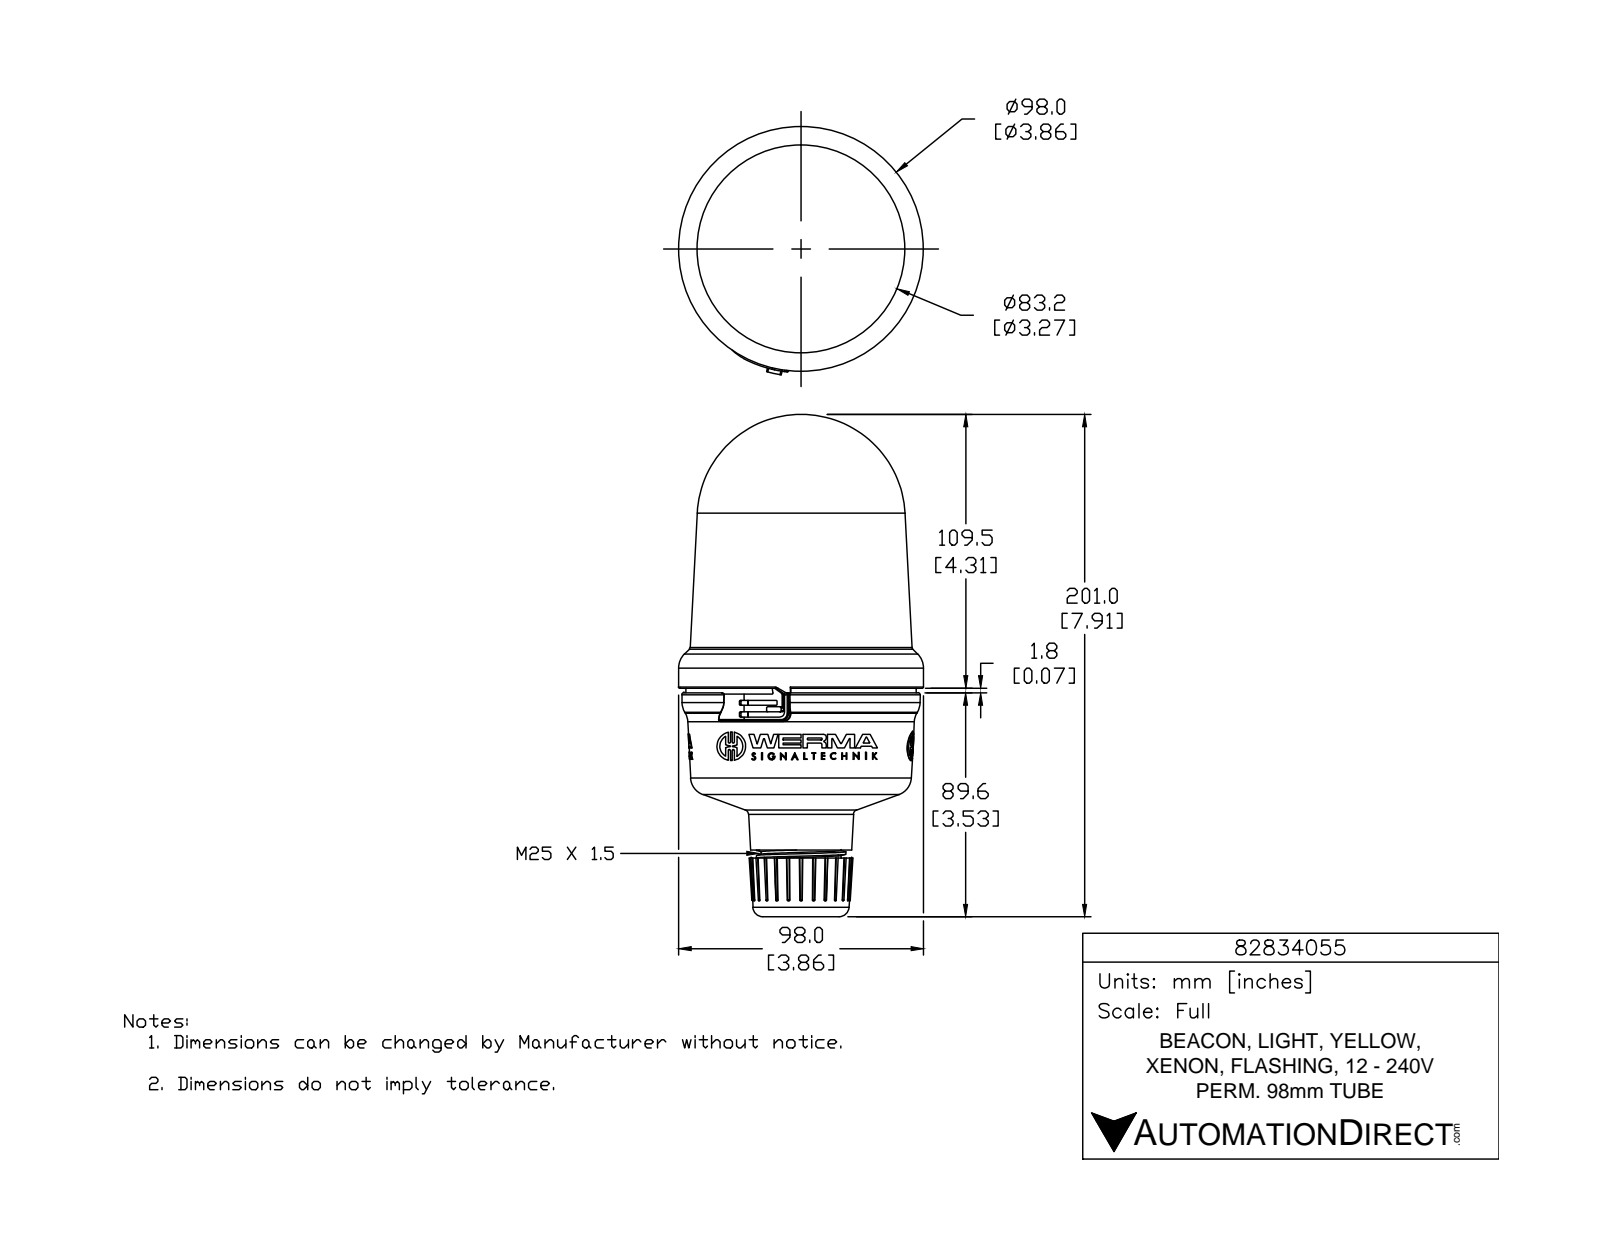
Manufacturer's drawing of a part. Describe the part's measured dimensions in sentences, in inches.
The part is named "82834055". Its 3-D file was written by "SolidWorks 2015 (AUTOMOTIVE_DESIGN)". It is 1 solid with 1006 faces: 554 planar, 189 cylindrical and 263 other. Overall it measures 7.914 by 3.912 by 3.858 inches. Its volume is 54.7 cubic inches and its surface area 91.39 square inches. Round holes: 3 of diameter 0.078, 1 of diameter 1.013, 1 of diameter 1.024. Round bosses or shafts: 3 of diameter 0.452, 3 of diameter 0.113, 1 of diameter 3.858, 1 of diameter 1.409, 1 of diameter 1.261. Partial cylindrical surfaces (rounded edges, fillets, slot ends): 12 of radius 0.02, 9 of radius 0.007, 6 of radius 0.007, 6 of radius 0.016, 6 of radius 0.016, 6 of radius 0.016, 6 of radius 0.262, 3 of radius 0.006. The main face-to-face distances are 2.214, 0.462, 2.676, 0.335, 0.127, 2.548, 2.603, 2.476, 2.141, 0.073.
